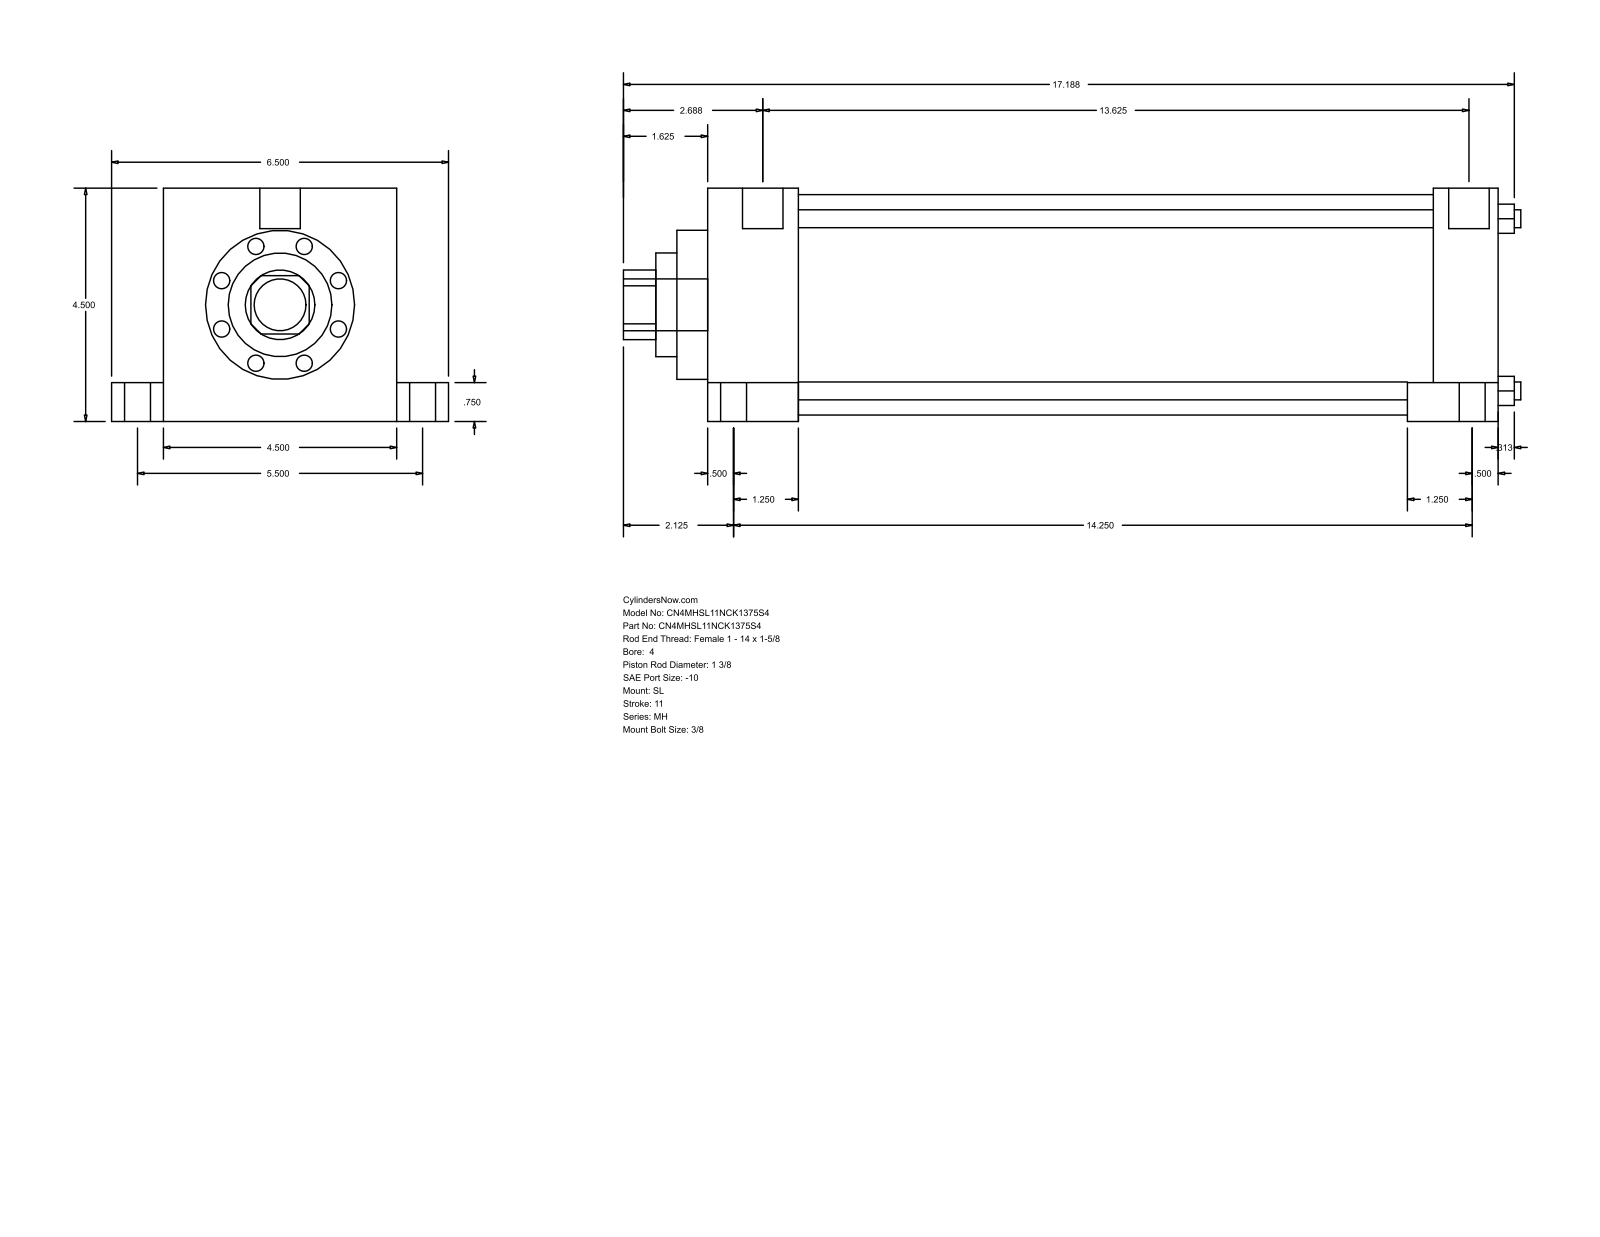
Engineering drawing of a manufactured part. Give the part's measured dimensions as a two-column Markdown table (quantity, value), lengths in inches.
| quantity | value |
| --- | --- |
| part name | MH_SL__0400_1.375 |
| STEP written by | GSSL Pune (CONFIG_CONTROL_DESIGN) |
| units | inches |
| bodies | 0 solids, 110 faces (77 planar, 33 cylindrical, 0 other) |
| overall size | 17.313 × 6.5 × 4.5 |
| round holes (diameter × count) | 0.345 × 4, 1.375 × 1, 2 × 1, 2.875 × 1, 4.25 × 1 |
| round bosses / shafts (diameter × count) | 0.75 × 4, 0.5 × 4, 0.344 × 4, 0.781 × 2, 1 × 1 |
| partial cylindrical surfaces (radius × count) | 0.672 × 1 |
| main face-to-face distances | 4.5, 15.25, 1.75, 13.5, 14, 12.25, 1.25, 1, 5.5, 0.75 |
| hole center spacings | 2.347, 3.32, 4.695 |
